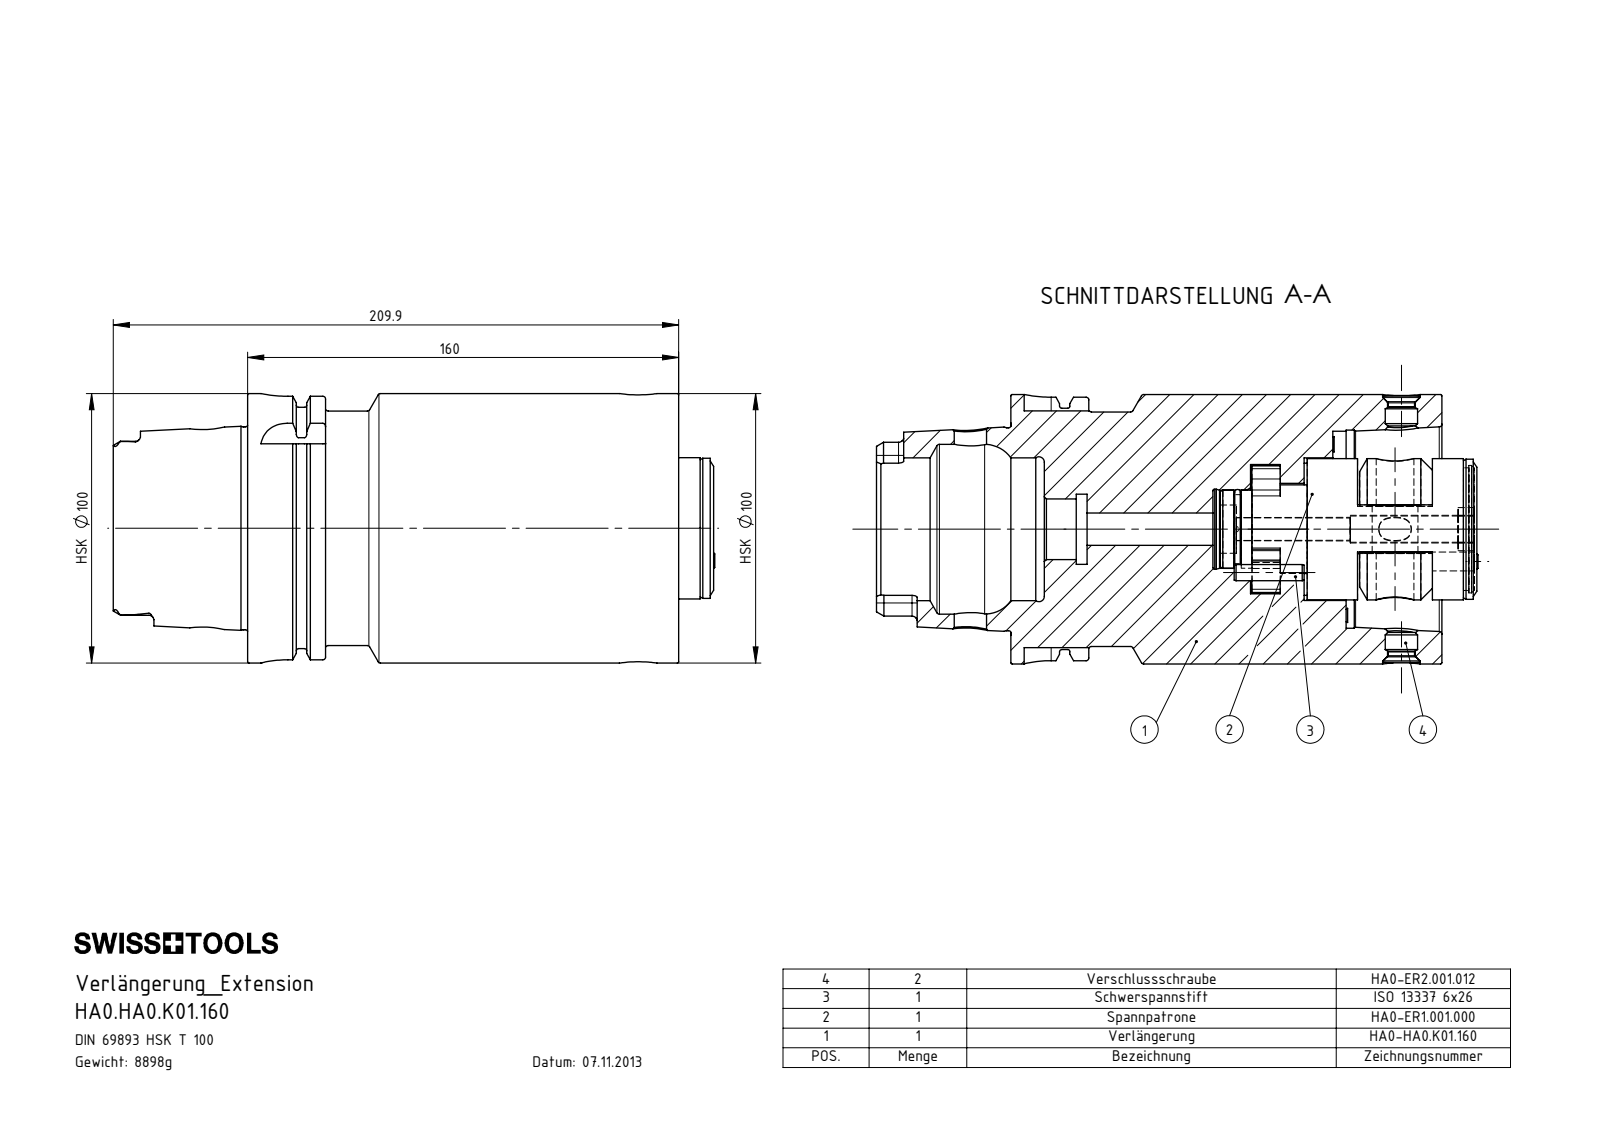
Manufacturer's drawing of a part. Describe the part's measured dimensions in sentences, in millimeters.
The part is named "HA0.HA0.K01.160; HA0-ER2.001.012; ISO 13337 - 6 x 26_Default; HA0-ER1.001.000 (+7 more)". Its 3-D file was written by "SolidWorks 2011 (AUTOMOTIVE_DESIGN)". It is 11 solids with 472 faces: 148 planar, 158 cylindrical and 166 other. Overall it measures 223.3 by 100 by 100 millimeters. Its volume is 1 133 000 cubic millimeters and its surface area 156 883 square millimeters. Round holes: 3 of diameter 10, 3 of diameter 14, 2 of diameter 8.5, 2 of diameter 12, 1 of diameter 4.5, 1 of diameter 6, 1 of diameter 7, 1 of diameter 10.25, 1 of diameter 17, 1 of diameter 17.9, 1 of diameter 22.5, 1 of diameter 26. Round bosses or shafts: 1 of diameter 100, 1 of diameter 91.95, 1 of diameter 87, 1 of diameter 75.26, 1 of diameter 52.4, 1 of diameter 52, 1 of diameter 47.3, 1 of diameter 32.9. Partial cylindrical surfaces (rounded edges, fillets, slot ends): 6 of radius 1.9, 6 of radius 4, 6 of radius 5, 4 of radius 4.85, 4 of radius 8, 4 of radius 10, 3 of radius 3, 2 of radius 4.83. The main face-to-face distances are 160, 108.9, 51.1, 60, 156.5, 47.6, 3.5, 71.05, 12.45, 96.45. The hole center spacings are 11, 16.28, 12, 13.68, 16.39, 20.82, 22, 28.99.
